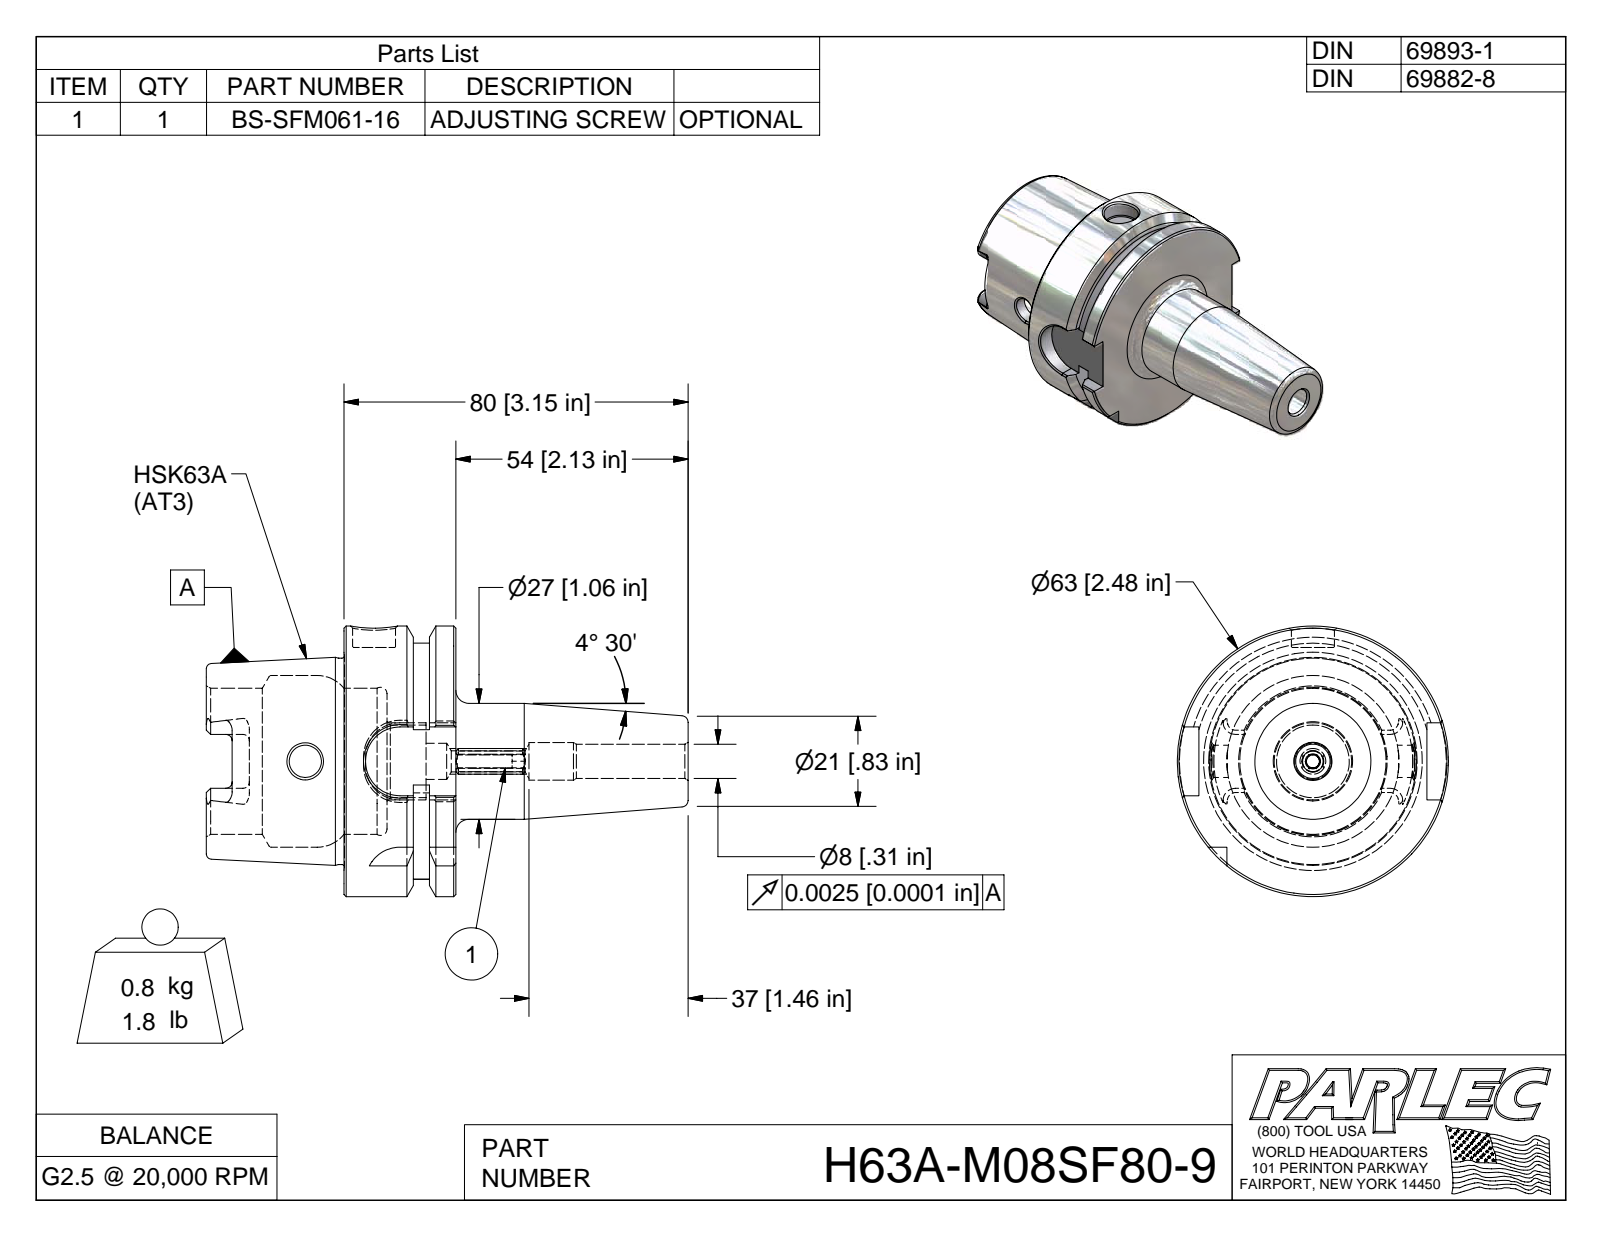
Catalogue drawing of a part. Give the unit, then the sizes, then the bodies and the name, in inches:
Units: inches
Overall size (bounding box): 4.409 × 2.48 × 2.48
Round holes (diameter × count): ⌀0.295 ×1, ⌀0.314 ×1, ⌀0.344 ×1, ⌀0.394 ×1, ⌀0.666 ×1, ⌀1.339 ×1, ⌀1.575 ×1
Round bosses / shafts (diameter × count): ⌀2.48 ×1, ⌀1.891 ×1, ⌀1.063 ×1
Partial cylindrical surfaces — rounded edges, fillets, slot ends (radius × count): R0.059 ×6, R0.113 ×4, R0.315 ×4, R0.118 ×1, R1.083 ×1
Main face-to-face distances: 1.024, 0.241, 0.389, 0.394, 0.63, 1.26, 1.654, 2.283, 1.894, 0.635
Volume: 6.488 in³ · Surface area: 43.22 in²
Bodies: 2 solids, 162 faces (58 planar, 35 cylindrical, 69 other)
Part name (STEP PRODUCT): H63A-M08SF80-9; H63A-M08SF80-9-1; BS-SFM061-16
STEP written by: Autodesk Inventor 2009 (AUTOMOTIVE_DESIGN)
